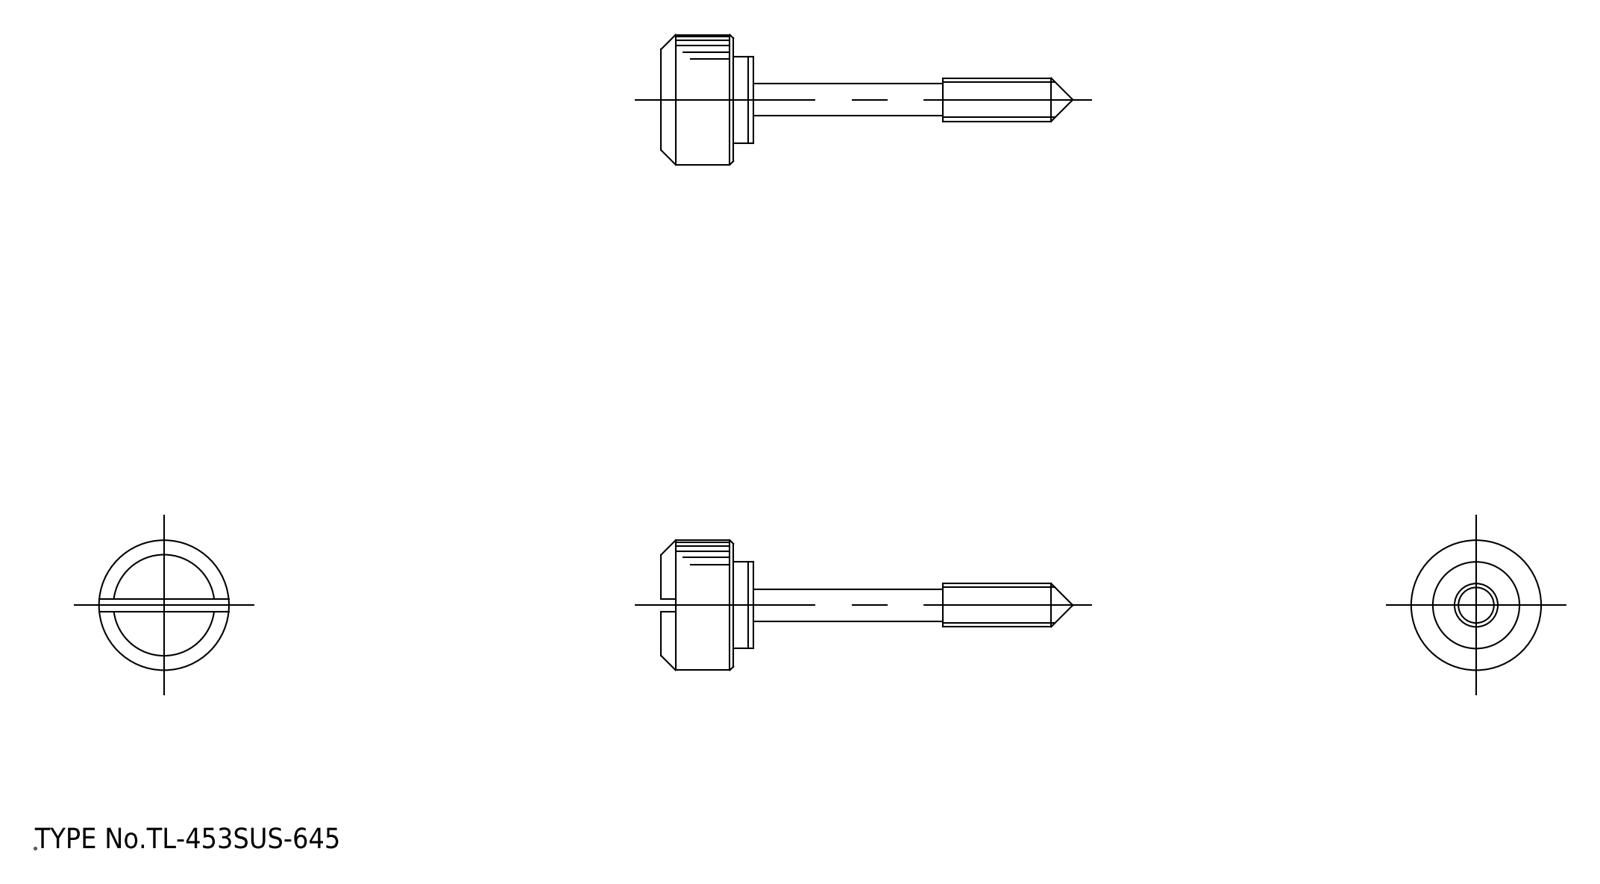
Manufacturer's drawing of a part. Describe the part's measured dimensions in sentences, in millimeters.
The part is named "washer; knob". Its 3-D file was written by "spGate 19.8.4 (****-****-****-****) (AUTOMOTIVE_DESIGN)". It is 2 solids with 42 faces: 18 planar, 18 cylindrical and 6 other. Overall it measures 57 by 18 by 18 millimeters. Its volume is 3 553 cubic millimeters and its surface area 2 042 square millimeters. Round bosses or shafts: 1 of diameter 18, 1 of diameter 12, 1 of diameter 6, 1 of diameter 4.5. Partial cylindrical surfaces (rounded edges, fillets, slot ends): 4 of radius 1, 1 of radius 2.3. The main face-to-face distances are 2, 10, 12, 12.8, 2.8, 0.8, 8, 10.8, 1.8, 39.
